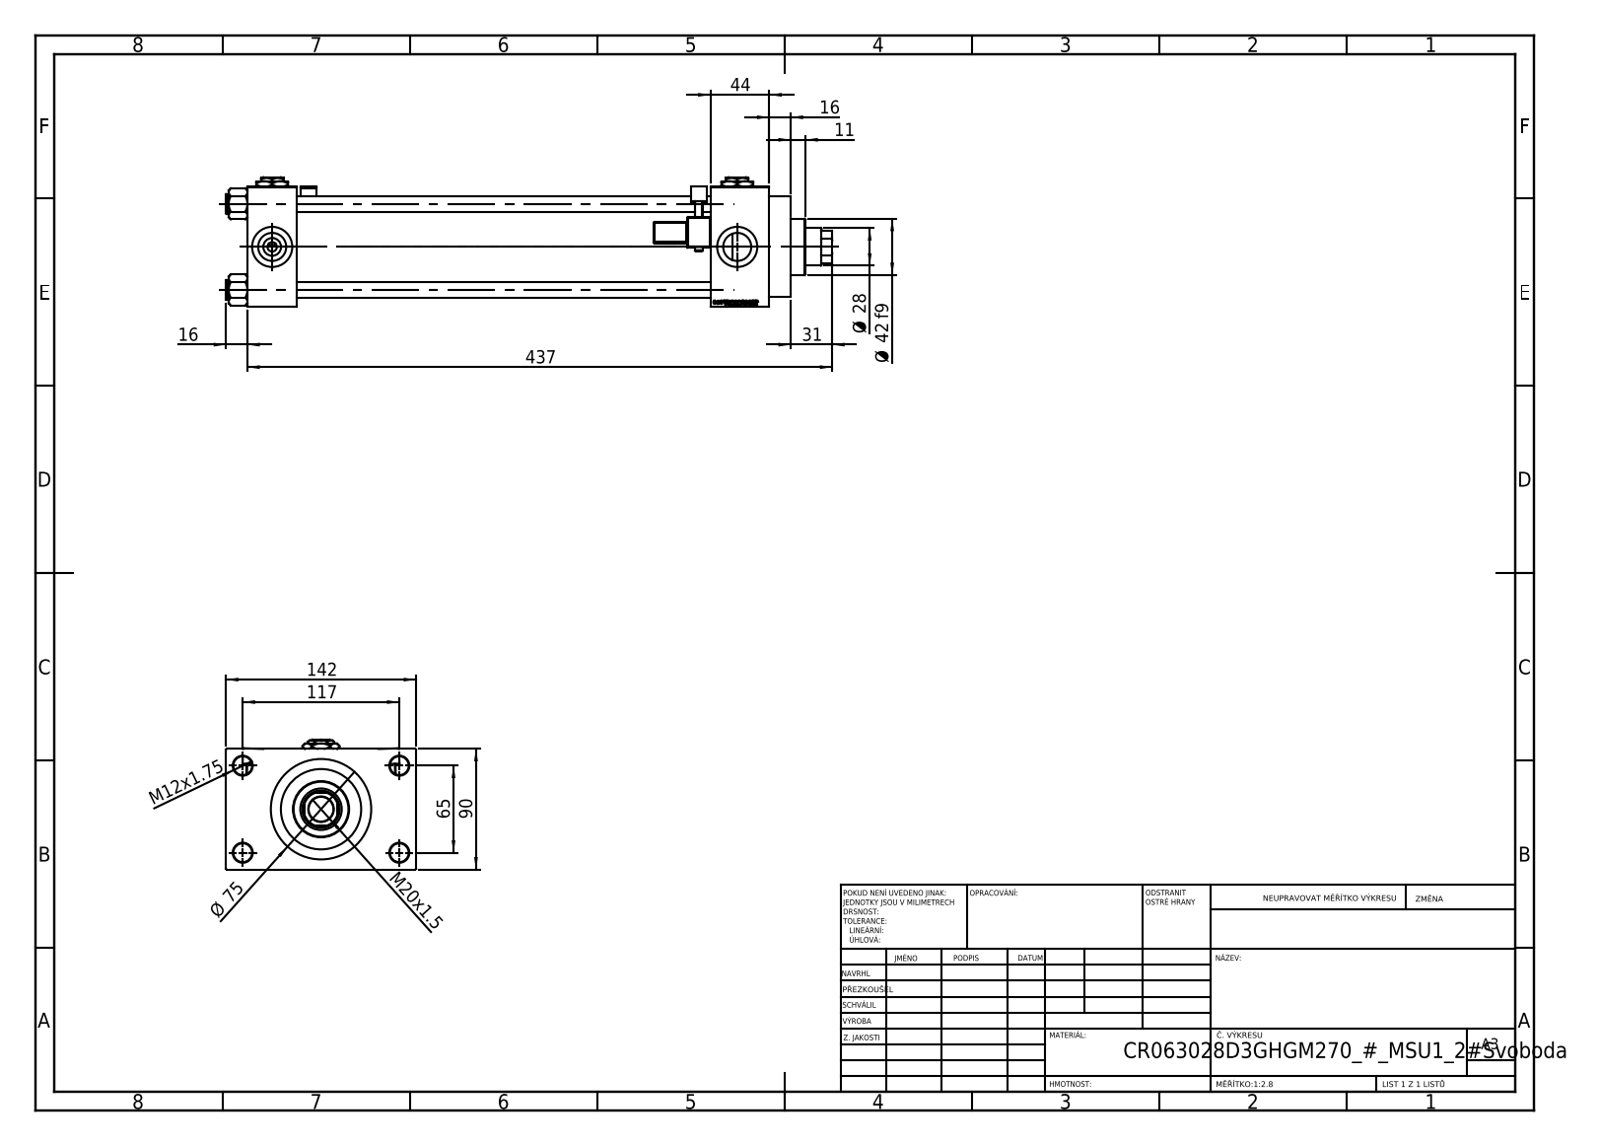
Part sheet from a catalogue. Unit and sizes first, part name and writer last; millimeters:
Units: millimetres
Overall size (bounding box): 453 × 142 × 97
Round holes (diameter × count): ⌀12 ×4, ⌀14 ×4, ⌀20.96 ×4, ⌀30 ×4, ⌀7 ×3, ⌀18.5 ×1, ⌀28 ×1, ⌀31 ×1, ⌀50 ×1, ⌀60 ×1, ⌀63 ×1
Round bosses / shafts (diameter × count): ⌀15 ×4, ⌀6 ×2, ⌀75 ×1, ⌀69 ×1, ⌀42 ×1
Partial cylindrical surfaces — rounded edges, fillets, slot ends (radius × count): R0.5 ×48, R1 ×2, R2.5 ×2, R4 ×2, R13.5 ×1
Main face-to-face distances: 90, 309, 37, 346, 390, 353, 44, 26, 116, 16
Hole centre spacings: 26.35, 45.47, 64.3, 66.92, 69.81, 90.65, 111.34, 65
Volume: 1 554 000 mm³ · Surface area: 380 573 mm²
Bodies: 15 solids, 1358 faces (603 planar, 159 cylindrical, 596 other)
Part name (STEP PRODUCT): V215CR_VCP_D; V215CR_D_Body; Zatka_pro_OIL_PORT; V215CR_D_TYCINKA (+3 more)
STEP written by: SolidWorks 2019 (CONFIG_CONTROL_DESIGN)
